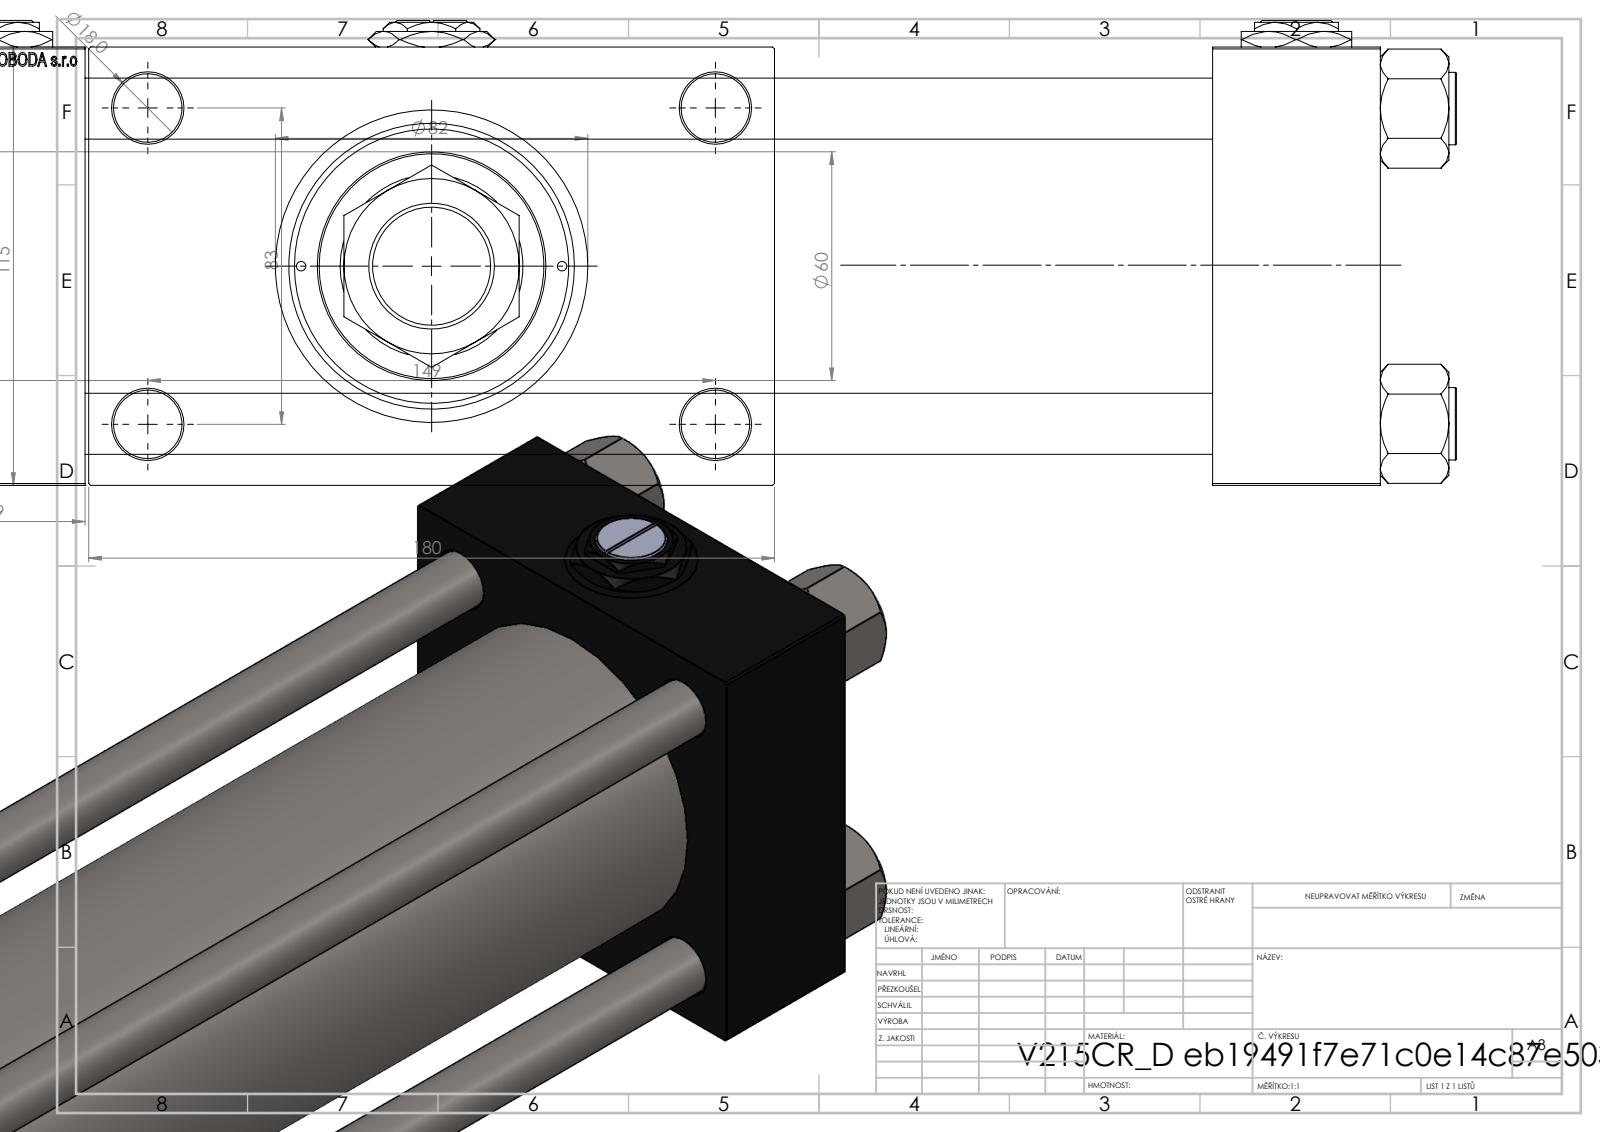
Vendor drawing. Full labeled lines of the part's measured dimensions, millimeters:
Part name (STEP PRODUCT): V215CR_D_TYCINKA; Zatka_pro_OIL_PORT; V215_VC_A; V215CR_VCP_D (+3 more)
STEP written by: SolidWorks 2019 (CONFIG_CONTROL_DESIGN)
Units: millimetres
Bodies: 14 solids, 1309 faces (610 planar, 107 cylindrical, 592 other)
Overall size (bounding box): 533 × 180 × 122
Volume: 2 809 000 mm³ · Surface area: 520 409 mm²
Round holes (diameter × count): ⌀16 ×4, ⌀18 ×4, ⌀26.44 ×4, ⌀35 ×4, ⌀7 ×3, ⌀2.5 ×2, ⌀31.5 ×1, ⌀45 ×1, ⌀48 ×1, ⌀61 ×1, ⌀72 ×1, ⌀80 ×1
Round bosses / shafts (diameter × count): ⌀19 ×4, ⌀86 ×1, ⌀82 ×1, ⌀60 ×1, ⌀33 ×1, ⌀31 ×1
Partial cylindrical surfaces — rounded edges, fillets, slot ends (radius × count): R22 ×1
Main face-to-face distances: 115, 296, 345, 49, 44, 340, 389, 32.5, 147.5, 46
Hole centre spacings: 33.15, 41.96, 57.81, 58.48, 82.7, 85.28, 86.17, 89.24
